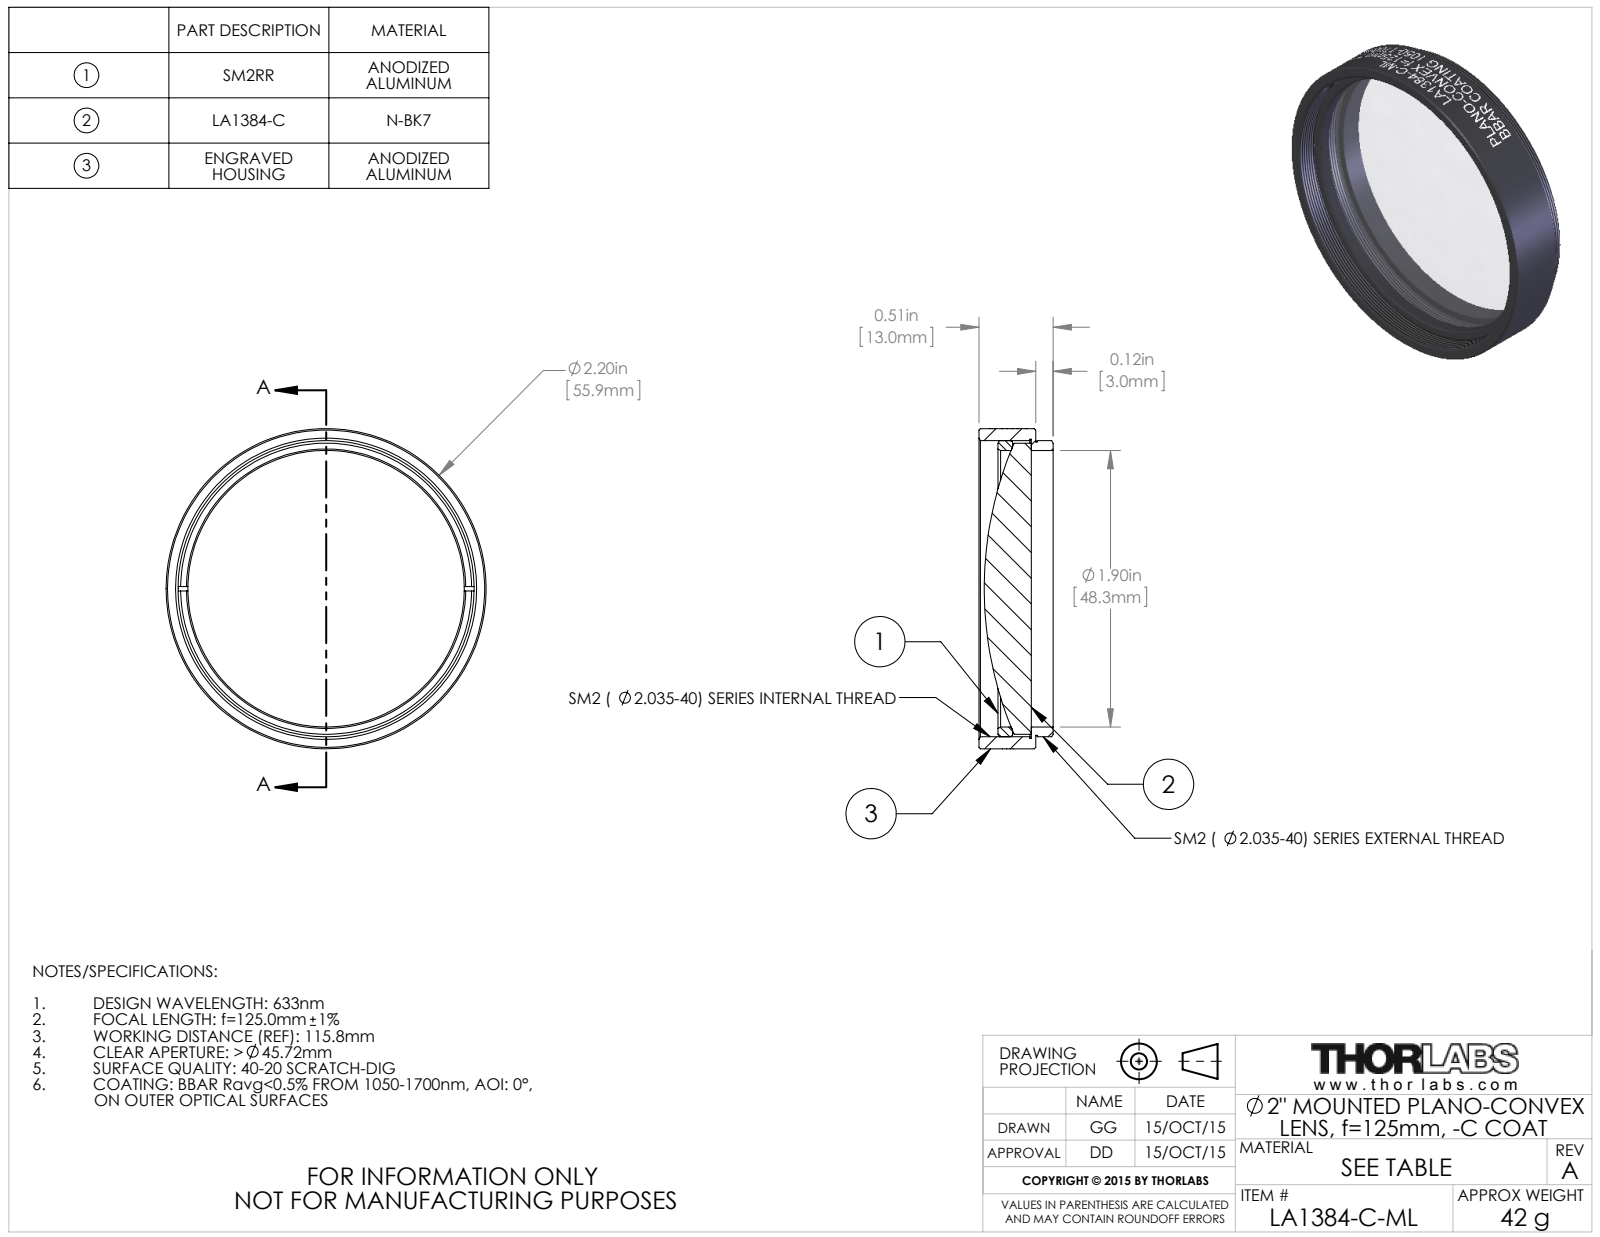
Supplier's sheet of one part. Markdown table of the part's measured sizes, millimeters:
| quantity | value |
| --- | --- |
| part name | TTN039579-E0W |
| STEP written by | SolidWorks 2014 (CONFIG_CONTROL_DESIGN) |
| units | millimeters |
| bodies | 3 solids, 148 faces (16 planar, 108 cylindrical, 24 other) |
| overall size | 55.9 × 55.9 × 13 |
| volume | 16 570 mm³ |
| surface area | 11 430 mm² |
| round holes (diameter × count) | 48.3 × 1, 52.2 × 1 |
| round bosses / shafts (diameter × count) | 55.9 × 1, 51.7 × 1, 51.2 × 1, 50.8 × 1 |
| main face-to-face distances | 0.8, 9.9, 9.1, 3, 3.8, 13, 7.1, 4, 3.3, 5.9 |
